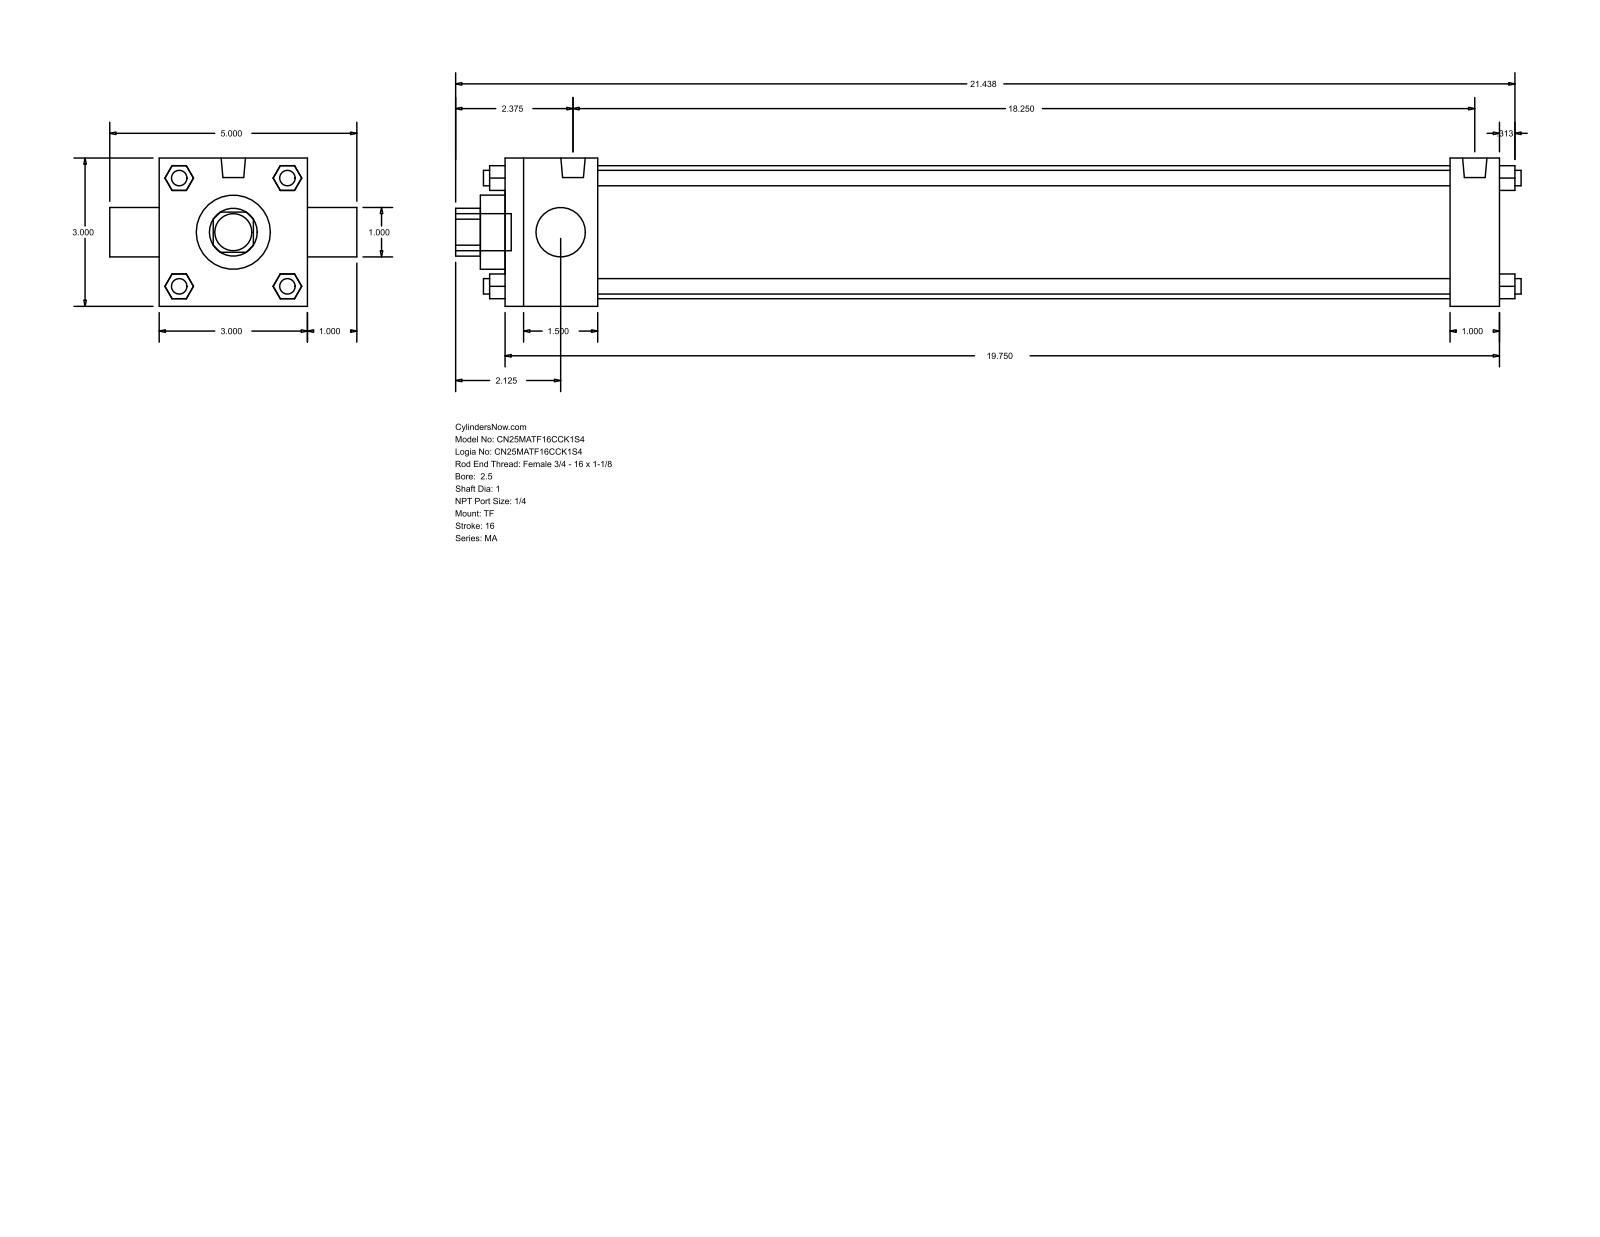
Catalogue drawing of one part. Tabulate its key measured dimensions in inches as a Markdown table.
| quantity | value |
| --- | --- |
| part name | MA_TF__0250_1 |
| STEP written by | GSSL Pune (CONFIG_CONTROL_DESIGN) |
| units | inches |
| bodies | 0 solids, 120 faces (92 planar, 28 cylindrical, 0 other) |
| overall size | 21.563 × 5 × 3 |
| round holes (diameter × count) | 1 × 2, 1.5 × 1, 2.69 × 1 |
| round bosses / shafts (diameter × count) | 0.313 × 7, 0.492 × 2, 0.75 × 1 |
| partial cylindrical surfaces (radius × count) | 0.484 × 1 |
| main face-to-face distances | 3, 20.125, 1, 0.5, 1.875, 19.125, 17.25, 18.25, 4, 1.095 |
